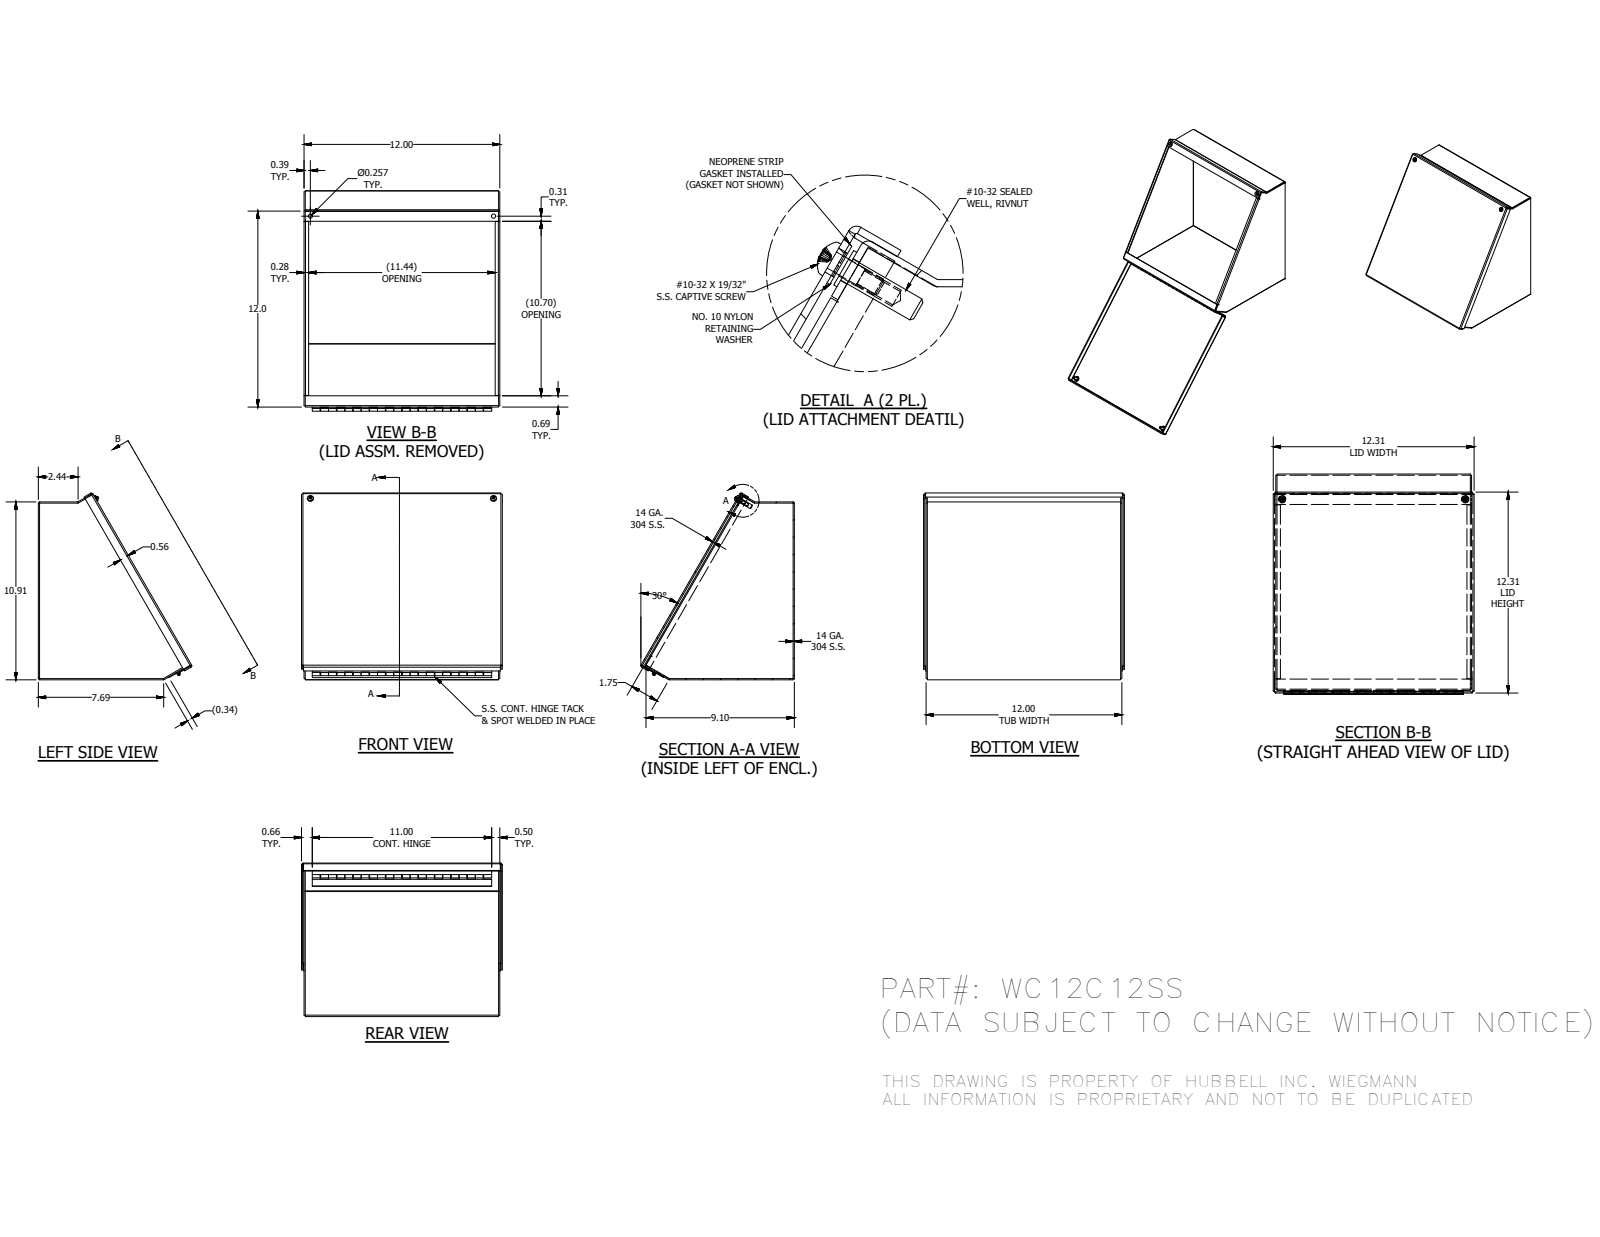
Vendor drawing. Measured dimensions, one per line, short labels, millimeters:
name: WC12C12SSBTB; WC12C12SSLID; WC12CSSLS; WC12CSSRS (+8 more)
written by: Autodesk Inventor 2014 (AUTOMOTIVE_DESIGN)
unit: mm
bodies: 13 solids, 407 faces (258 planar, 97 cylindrical, 52 other)
size: 312.74 × 290.87 × 239.09
volume: 753 661 mm³; area: 825 478 mm²
holes: 2× ⌀3.96, 2× ⌀4.98, 2× ⌀6.53, 2× ⌀7.06, 2× ⌀7.14, 1× ⌀2.96
bosses: 2× ⌀11.51, 2× ⌀10.31, 2× ⌀9.47, 2× ⌀6.3, 2× ⌀4.83, 1× ⌀5.08, 1× ⌀2.54
rounds: 12× R0.4, 12× R2.28, 2× R2.27
face distances: 1.88, 302.92, 304.8, 301.04, 275.14, 273.26, 277.02, 3.97, 306.89, 4.26
hole spacings: 285.14
